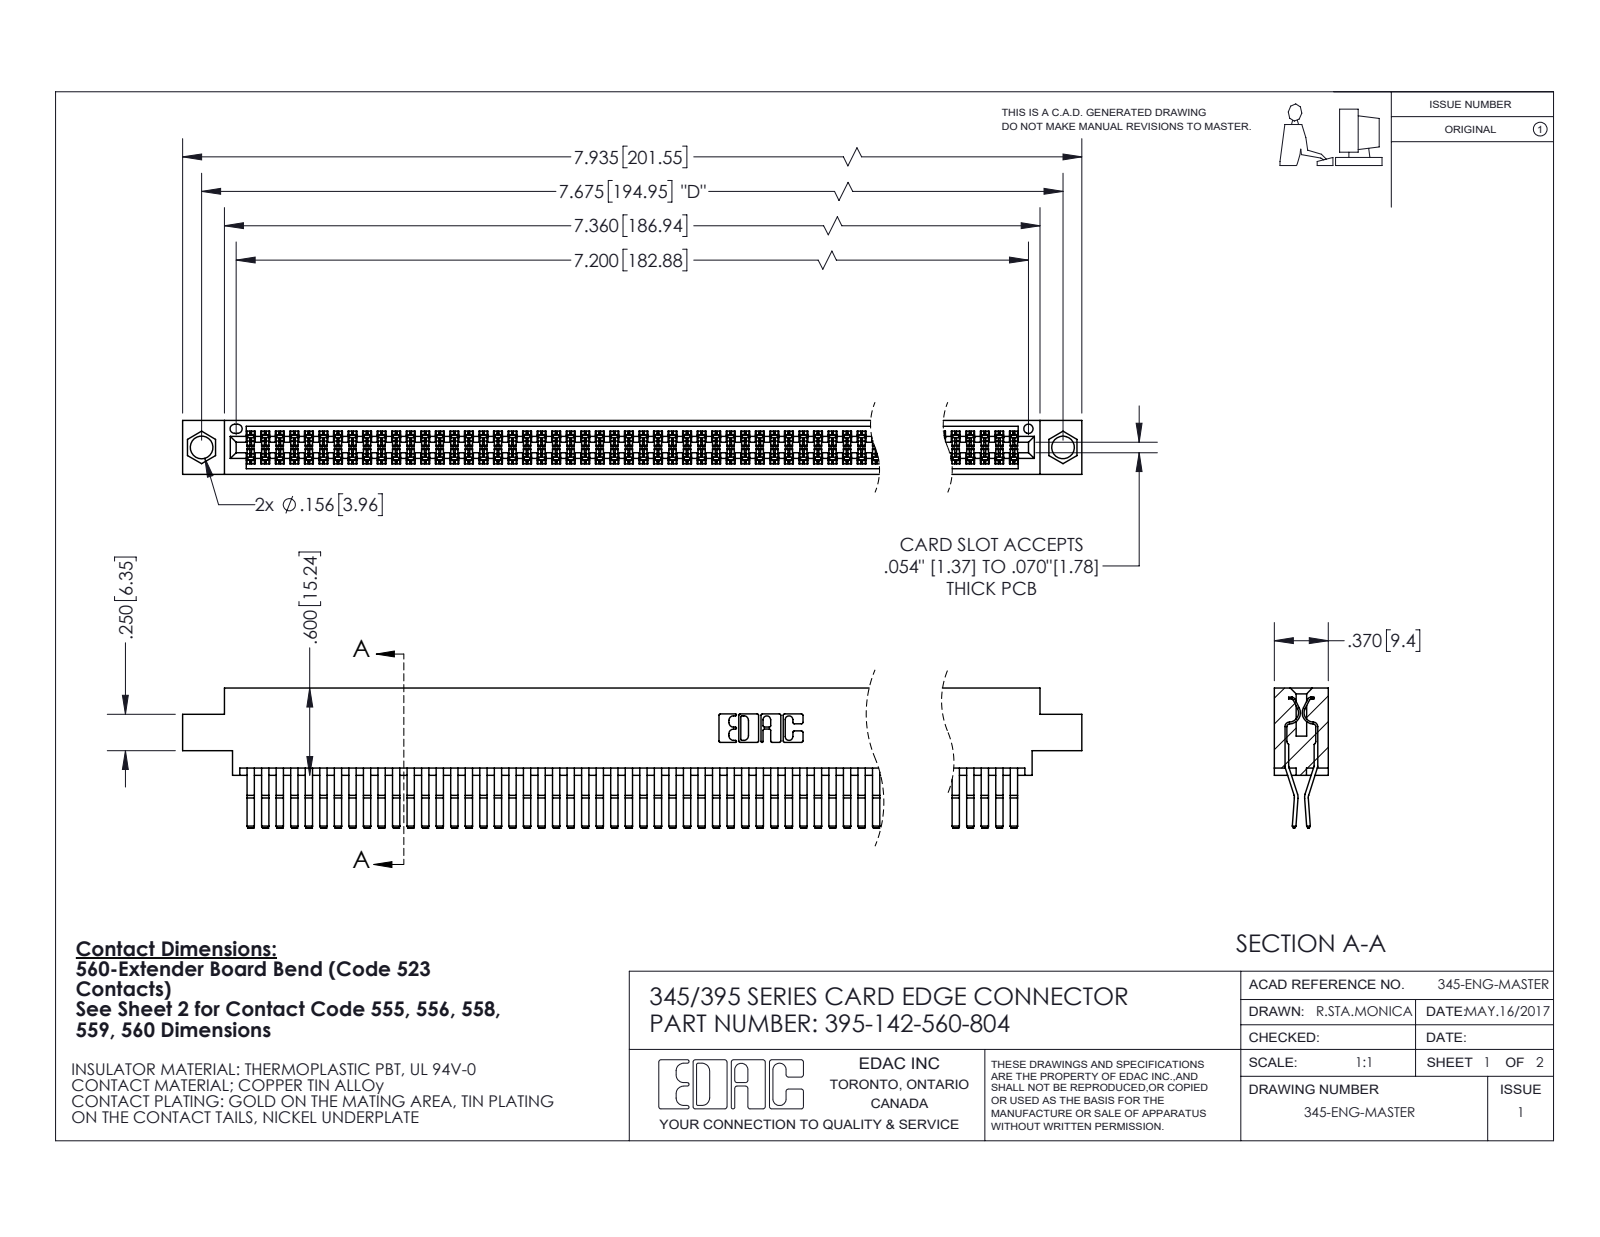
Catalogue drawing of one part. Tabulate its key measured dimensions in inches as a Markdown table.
| quantity | value |
| --- | --- |
| part name | 345 Part_0.170 Offset - 0.156 Dia-TI; 345-292-001_560 Tail; 395-142-560-804 |
| STEP written by | SolidWorks 2020 (CONFIG_CONTROL_DESIGN) |
| units | inches |
| bodies | 143 solids, 7528 faces (4784 planar, 2744 cylindrical, 0 other) |
| overall size | 7.935 × 0.962 × 0.37 |
| volume | 1.255 in³ |
| surface area | 51.68 in² |
| round holes (diameter × count) | 0.156 × 2, 0.064 × 1 |
| partial cylindrical surfaces (radius × count) | 0.006 × 284, 0.01 × 22, 0.007 × 6, 0.031 × 6, 0.026 × 3, 0.01 × 2, 0.014 × 2, 0.019 × 2 |
| main face-to-face distances | 0.025, 0.072, 0.298, 0.37, 0.2, 0.098, 0.272, 0.225, 0.175, 0.149 |
| hole center spacings | 0.27, 7.439, 7.675 |
